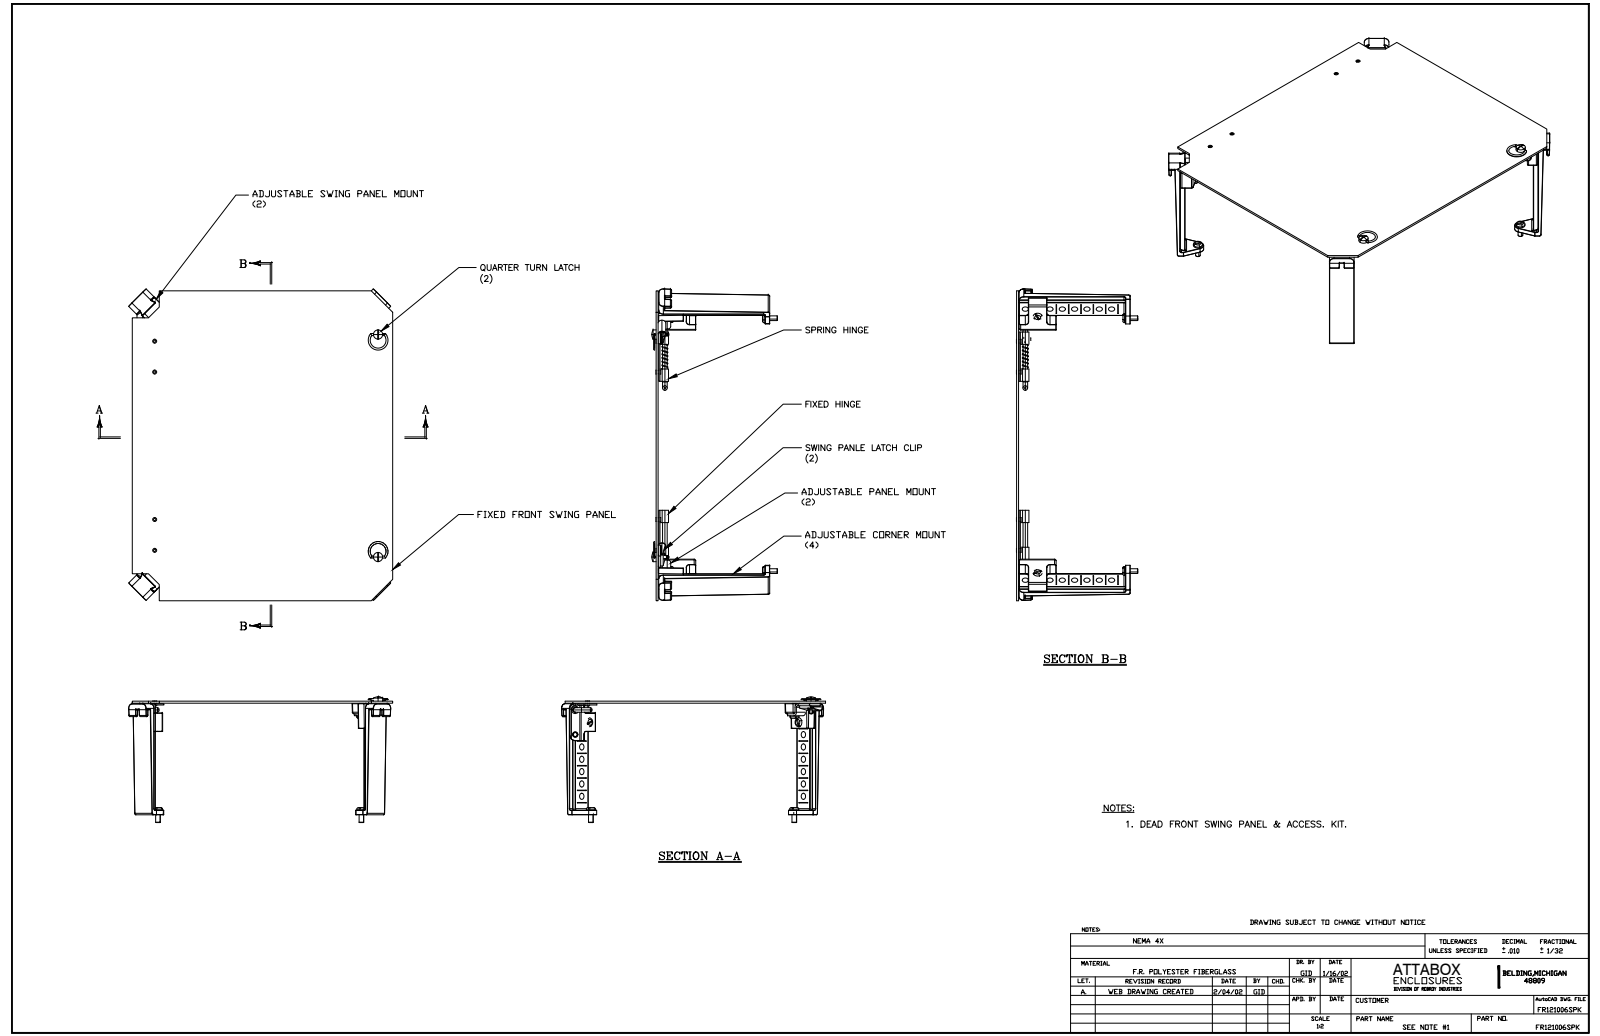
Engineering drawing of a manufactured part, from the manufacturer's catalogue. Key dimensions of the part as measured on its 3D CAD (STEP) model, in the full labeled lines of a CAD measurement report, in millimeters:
Part name (STEP PRODUCT): FR121006SPK
STEP written by: SolidWorks 2019 (AUTOMOTIVE_DESIGN)
Units: millimetres
Bodies: 48 solids, 1805 faces (834 planar, 477 cylindrical, 494 other)
Overall size (bounding box): 320.6 × 272.2 × 131.6
Volume: 316 800 mm³ · Surface area: 255 300 mm²
Round holes (diameter × count): ⌀6.4 ×36, ⌀4 ×6, ⌀6.4 ×6, ⌀1.3 ×4, ⌀3.6 ×4, ⌀3.7 ×4, ⌀5.5 ×4, ⌀5.6 ×4, ⌀7.9 ×3, ⌀5 ×2, ⌀8.9 ×2, ⌀3.9 ×1
Round bosses / shafts (diameter × count): ⌀4.8 ×10, ⌀9.5 ×6, ⌀6.2 ×6, ⌀11 ×4, ⌀8 ×4, ⌀4.1 ×4, ⌀2 ×4, ⌀10 ×2
Partial cylindrical surfaces — rounded edges, fillets, slot ends (radius × count): R0.3 ×212, R1.5 ×44, R1.6 ×16, R0.6 ×8, R3.3 ×6, R1.2 ×4, R4.8 ×4, R5.8 ×4
Main face-to-face distances: 2, 358.7, 5.2, 363.9, 4.2, 2.2, 25.4, 179.2, 189.8, 174.1
Hole centre spacings: 38.1, 12.7, 25.4, 44, 52.3, 35.9, 50.8, 62.2
